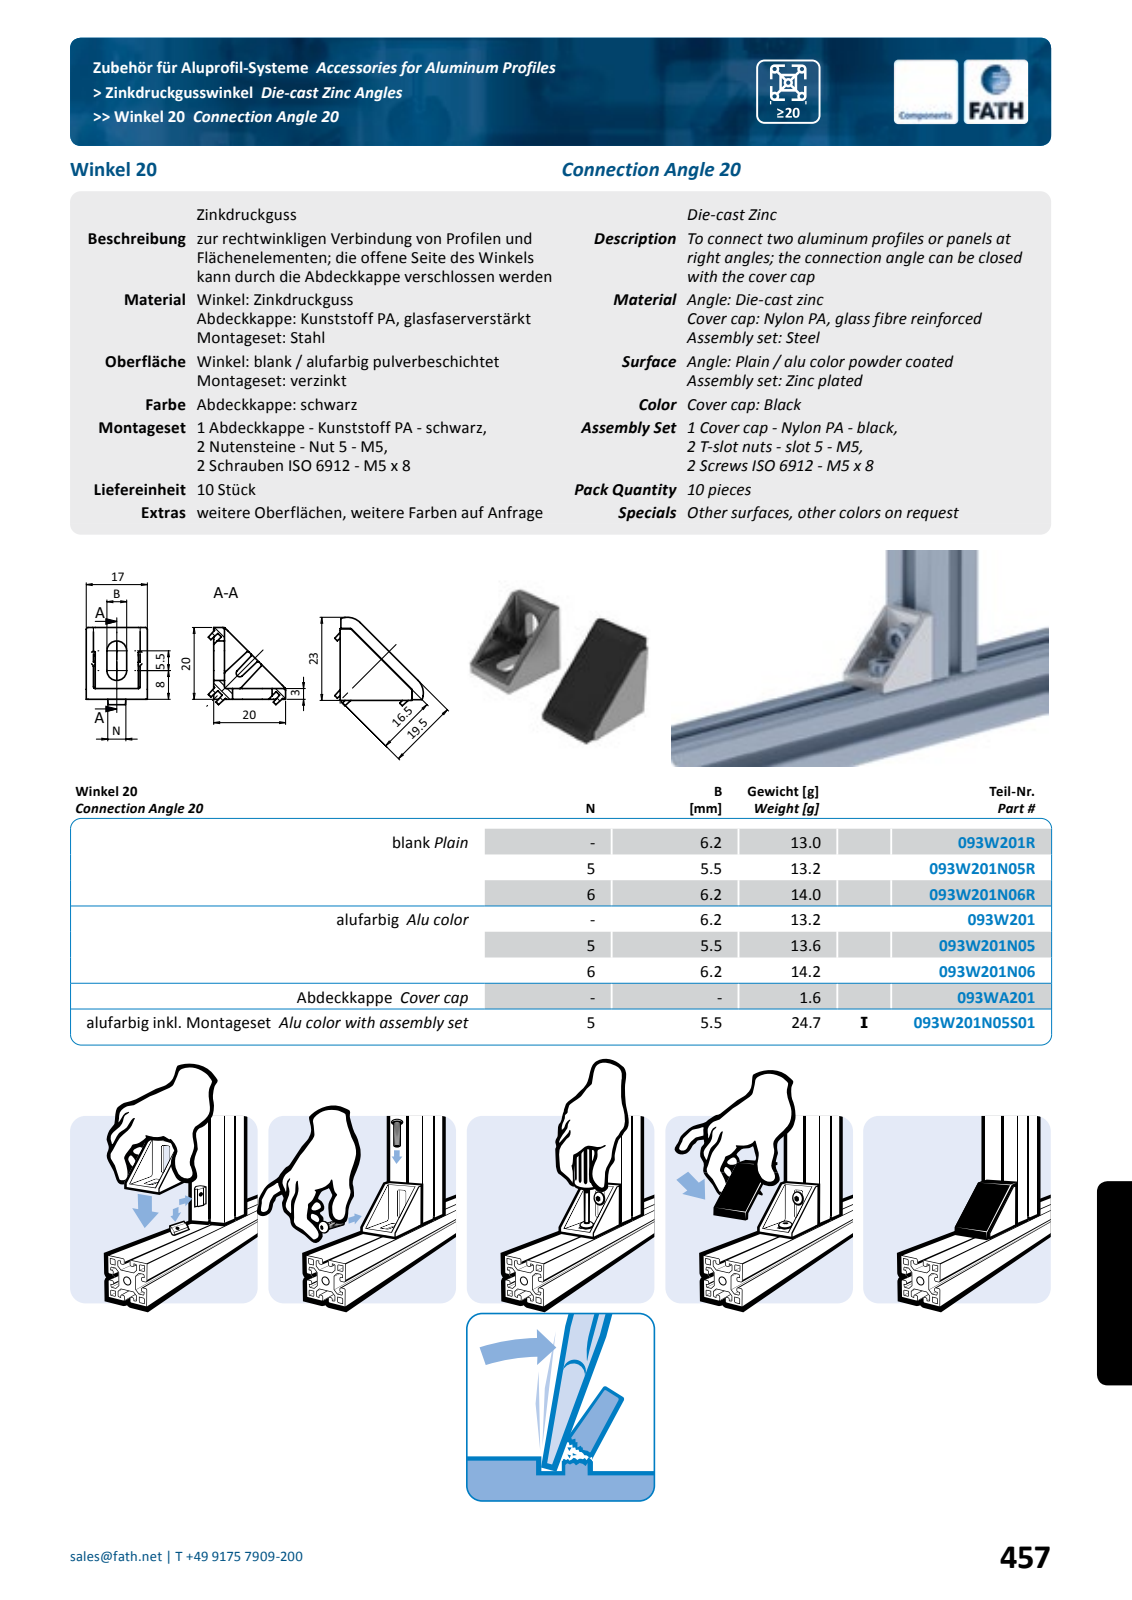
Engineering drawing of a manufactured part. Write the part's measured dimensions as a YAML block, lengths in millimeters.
part_name: "fath_093w201n05r"
step_written_by: "Spatial InterOp 3D (automotive_design)"
units: millimeters
bodies: {solids: 1, faces: 165, planar: 61, cylindrical: 68, other: 36}
overall_size: [21.5, 21.5, 17]
volume: 2043
surface_area: 2207
partial_cylinders:
  - {radius: 0.5, count: 21}
  - {radius: 0.2, count: 17}
  - {radius: 1, count: 4}
  - {radius: 2.75, count: 4}
  - {radius: 1, count: 1}
face_to_face_distances: [17, 3, 2, 15, 20, 2.5, 14.5, 0.5, 12.5, 13]
